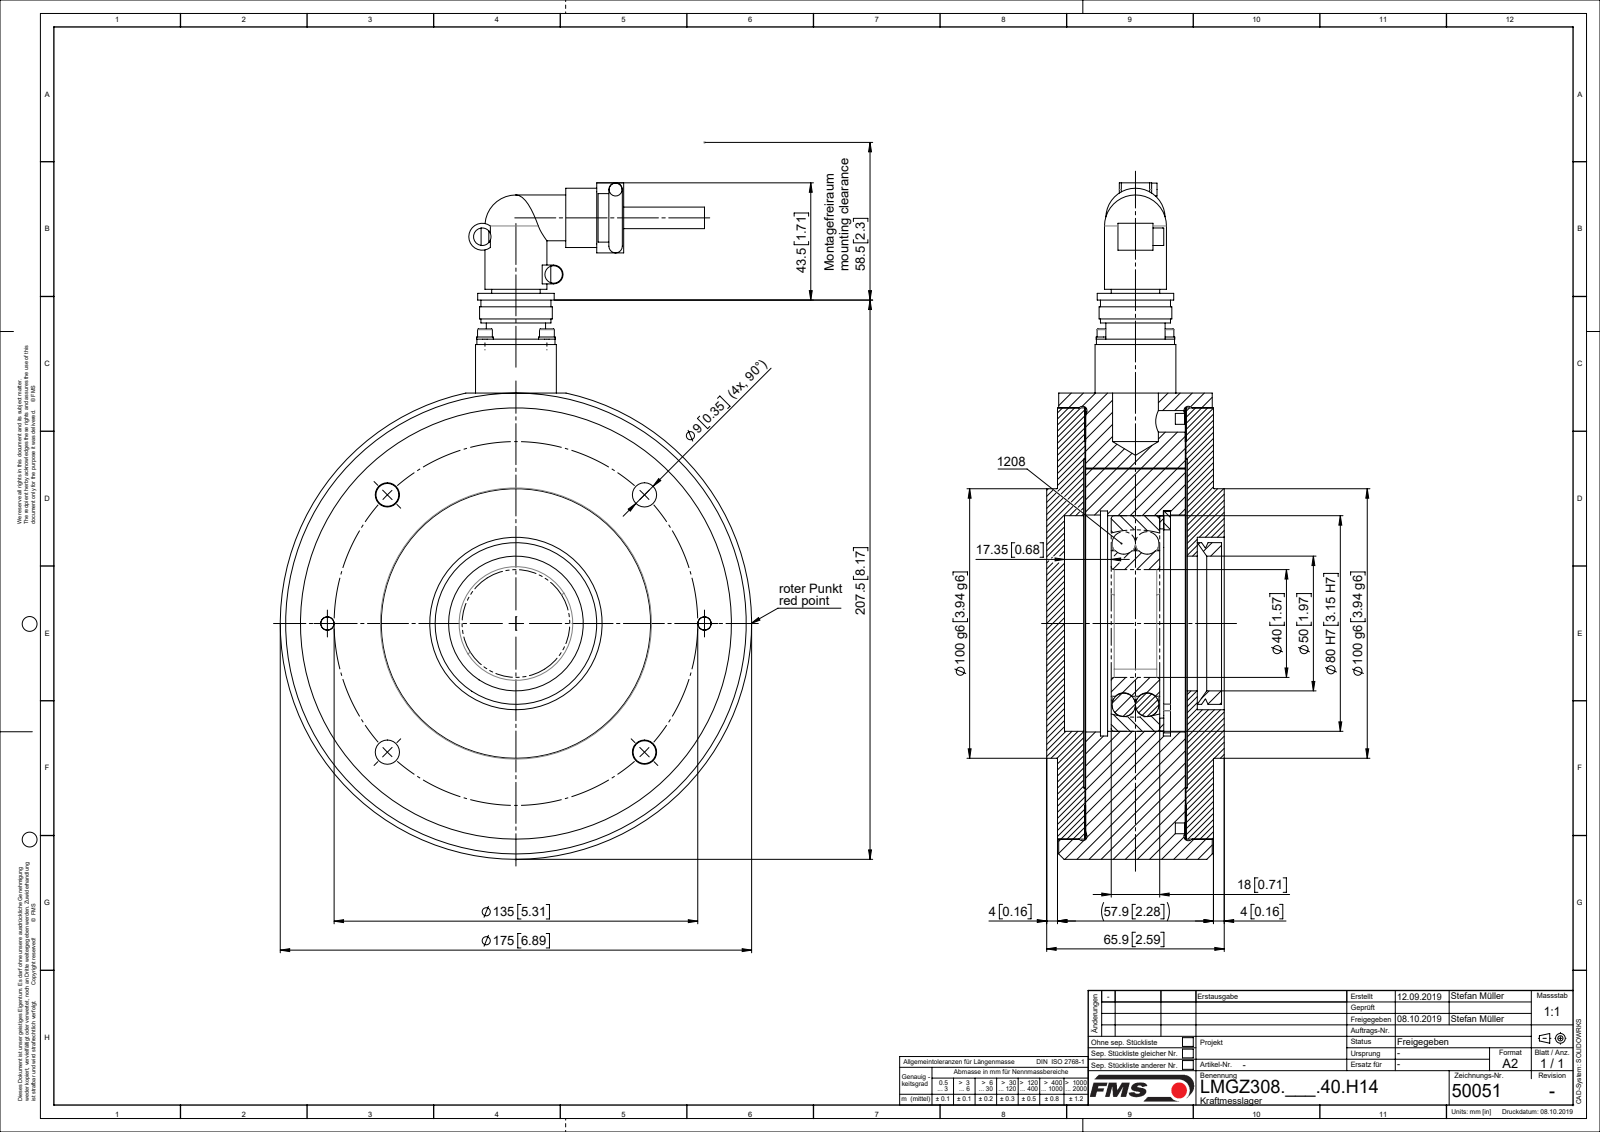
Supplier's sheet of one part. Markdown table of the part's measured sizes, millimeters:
| quantity | value |
| --- | --- |
| part name | L50051; L4857104; ~TEIL1; L49015 (+8 more) |
| STEP written by | Mechanical Desktop 2007 (CONFIG_CONTROL_DESIGN) |
| units | millimeters |
| bodies | 22 solids, 397 faces (113 planar, 233 cylindrical, 51 other) |
| overall size | 251 × 175 × 65.9 |
| volume | 1 278 000 mm³ |
| surface area | 276 492 mm² |
| round holes (diameter × count) | 2.6 × 4, 3.2 × 4, 3.4 × 4, 3.5 × 4, 9 × 4, 5.15 × 2, 6.6 × 2, 8.68 × 2, 11 × 2, 23 × 1, 40 × 1, 48 × 1 |
| round bosses / shafts (diameter × count) | 6.2 × 4, 5.5 × 4, 3 × 4, 22 × 2, 10 × 2, 6.5 × 2, 6 × 2, 4.8 × 2 |
| partial cylindrical surfaces (radius × count) | 2.5 × 2, 7.5 × 2, 3.5 × 1, 5 × 1 |
| main face-to-face distances | 37.25, 10.2, 10.45, 47.45, 47.7, 37, 37.5, 0.5, 4, 38 |
| hole center spacings | 16.26, 23, 52.67, 67.5, 95.46, 127.04, 32.53, 70 |
